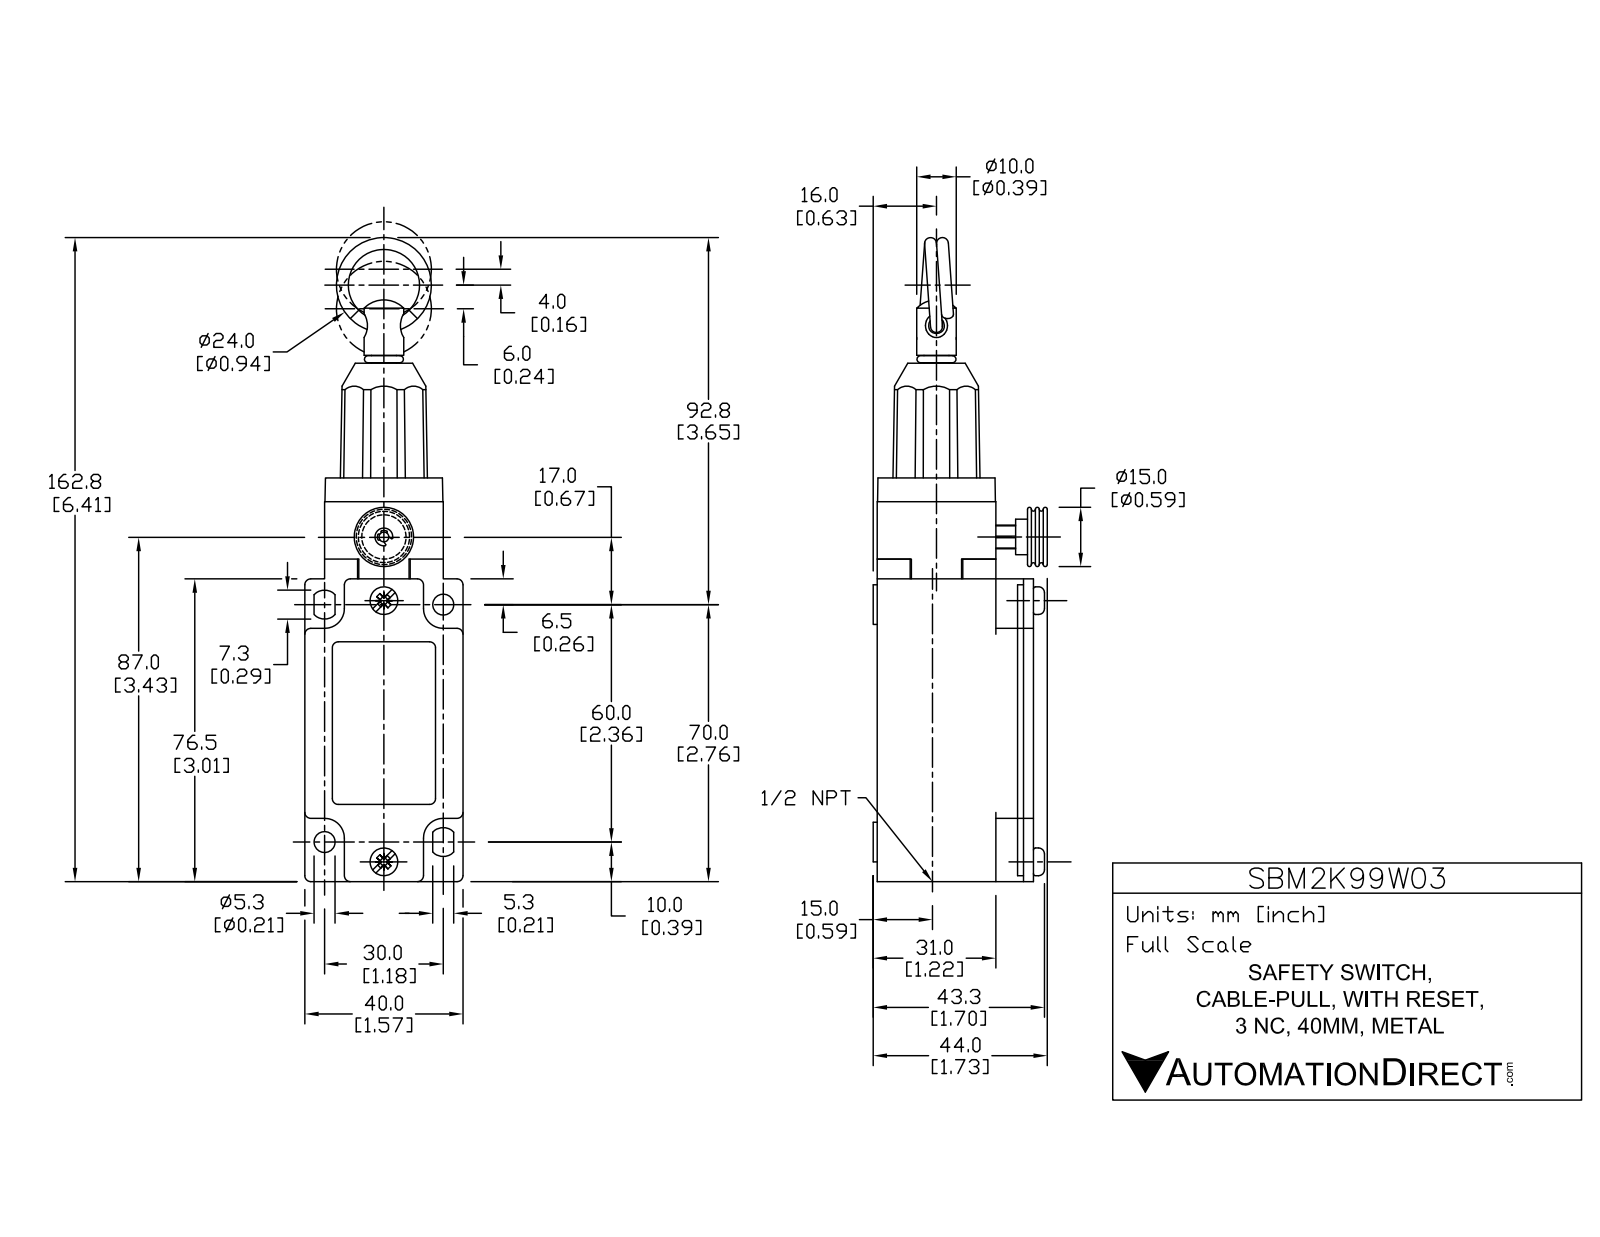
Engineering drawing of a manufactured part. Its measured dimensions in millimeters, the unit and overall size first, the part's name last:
Units: millimetres
Overall size (bounding box): 164 × 43.8 × 40
Round holes (diameter × count): ⌀5.2 ×2, ⌀4 ×1, ⌀10.1 ×1, ⌀17 ×1, ⌀18 ×1, ⌀19 ×1
Round bosses / shafts (diameter × count): ⌀10 ×5, ⌀7 ×2, ⌀17.8 ×1, ⌀9.8 ×1, ⌀6.7 ×1, ⌀6.3 ×1, ⌀2.5 ×1
Partial cylindrical surfaces — rounded edges, fillets, slot ends (radius × count): R1.5 ×16, R5 ×4, R3.3 ×2, R11.5 ×1, R12 ×1
Main face-to-face distances: 40, 5, 30, 39.5, 35, 9.5, 76.5, 1, 26, 25
Hole centre spacings: 1, 67.1
Volume: 142 500 mm³ · Surface area: 30 610 mm²
Bodies: 5 solids, 233 faces (91 planar, 88 cylindrical, 54 other)
Part name (STEP PRODUCT): SBM2K99W03
STEP written by: SolidWorks 2017 (AUTOMOTIVE_DESIGN)
